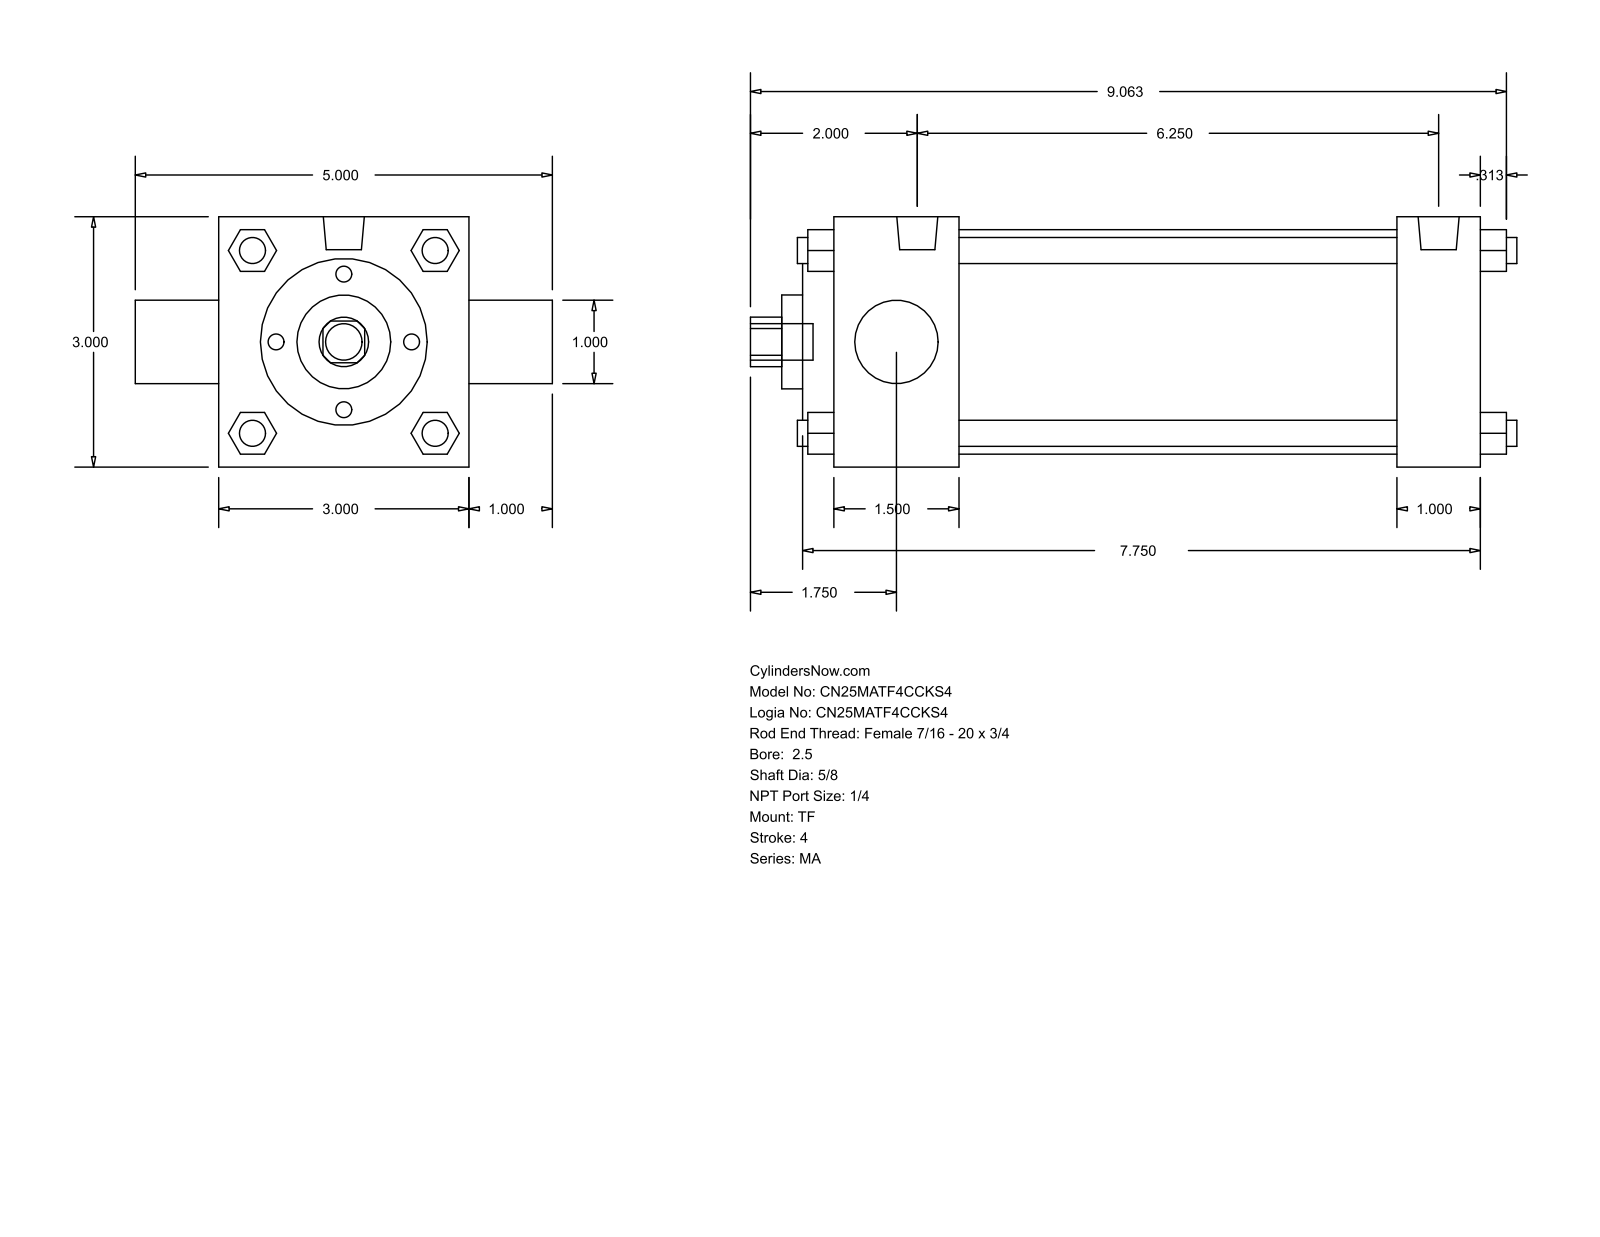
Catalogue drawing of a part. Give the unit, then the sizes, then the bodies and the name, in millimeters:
Units: millimetres
Overall size (bounding box): 233.36 × 127 × 76.2
Round holes (diameter × count): ⌀15.88 ×1, ⌀25.4 ×1, ⌀28.57 ×1, ⌀50.8 ×1, ⌀68.33 ×1
Round bosses / shafts (diameter × count): ⌀7.94 ×7, ⌀12.49 ×2, ⌀11.11 ×1
Partial cylindrical surfaces — rounded edges, fillets, slot ends (radius × count): R7.54 ×1
Main face-to-face distances: 76.2, 196.85, 25.4, 38.1, 171.45, 133.35, 158.75, 12.7, 9.52, 47.62
Bodies: 0 solids, 122 faces (93 planar, 29 cylindrical, 0 other)
Part name (STEP PRODUCT): MA_TF__0250_0.625
STEP written by: GSSL Pune (CONFIG_CONTROL_DESIGN)
